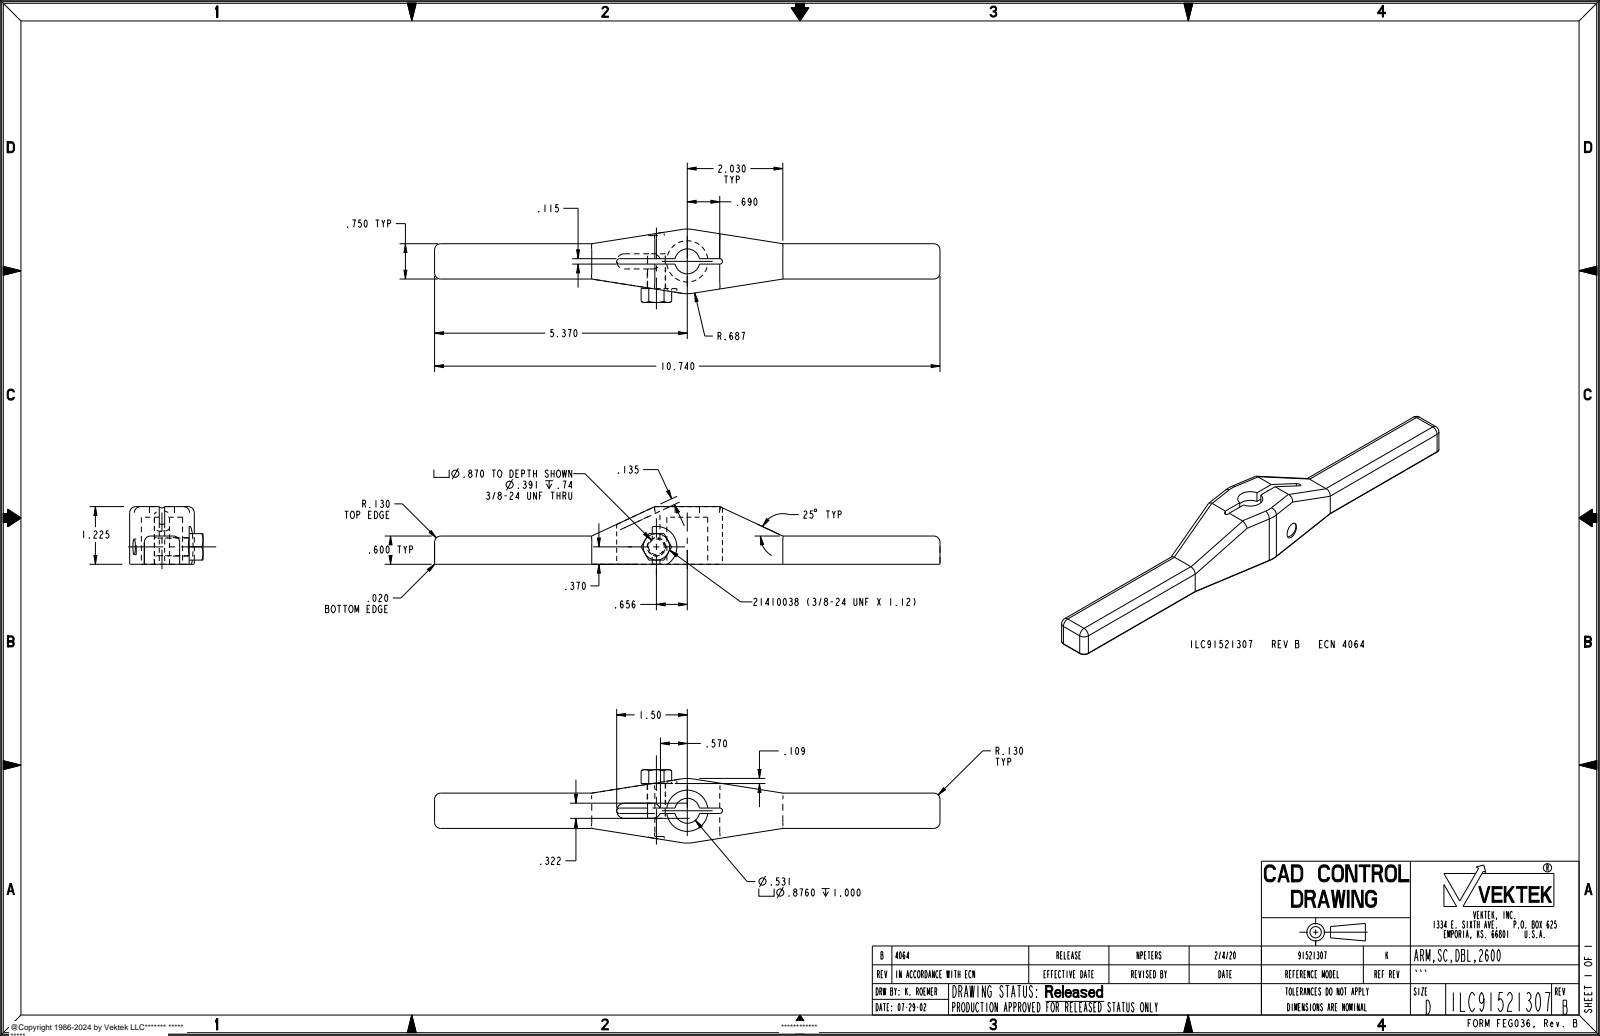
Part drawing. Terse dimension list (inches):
name: ILC91521307
written by: PRO/ENGINEER BY PARAMETRIC TECHNOLOGY CORPORATION, 2013320 (AUTOMOTIVE_DESIGN)
unit: in
bodies: 1 solid, 105 faces (37 planar, 50 cylindrical, 18 other)
size: 10.74 × 1.56 × 1.225
volume: 6.584 in³; area: 42.23 in²
holes: 1× ⌀0.332, 1× ⌀0.391, 1× ⌀0.531, 1× ⌀0.876
bosses: 1× ⌀0.375
rounds: 16× R0.13, 8× R0.02, 2× R0.057, 2× R0.161, 1× R0.435, 1× R0.687
face distances: 0.6, 0.75, 1.374, 0.317, 0.432, 1.225, 0.625, 0.214, 0.536, 0.104
